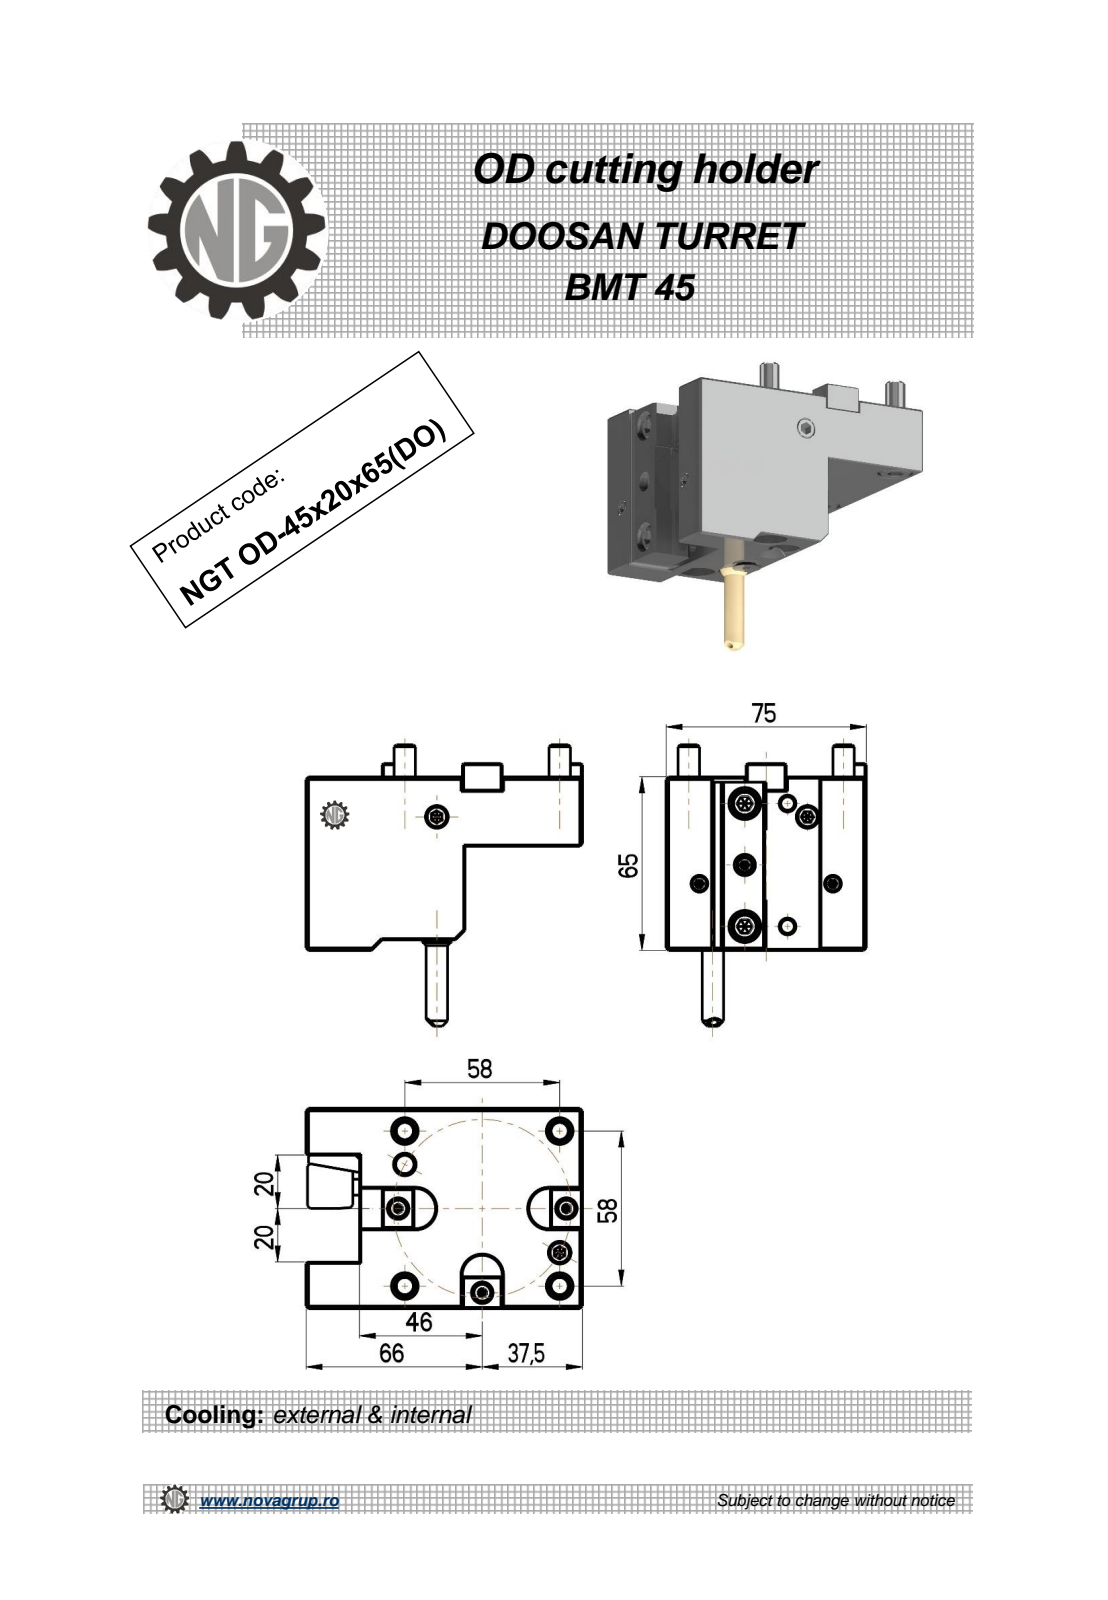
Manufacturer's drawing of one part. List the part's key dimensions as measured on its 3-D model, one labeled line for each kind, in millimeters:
Part name (STEP PRODUCT): NGT_OD_45_20_65_DO
STEP written by: PRO/ENGINEER BY PARAMETRIC TECHNOLOGY CORPORATION, 2010280 (CONFIG_CONTROL_DESIGN)
Units: millimetres
Bodies: 1 solid, 207 faces (135 planar, 38 cylindrical, 34 other)
Overall size (bounding box): 105.34 × 103.5 × 75
Volume: 338 180 mm³ · Surface area: 42 402 mm²
Round holes (diameter × count): ⌀3 ×1, ⌀5 ×1, ⌀6.8 ×1
Round bosses / shafts (diameter × count): ⌀8 ×5, ⌀6 ×3, ⌀11.2 ×1
Partial cylindrical surfaces — rounded edges, fillets, slot ends (radius × count): R0.22 ×6, R0.41 ×6, R7.5 ×3
Main face-to-face distances: 75, 26, 20, 39.5, 59.5, 61, 35, 44, 103.5, 83.5
Hole centre spacings: 12.5
